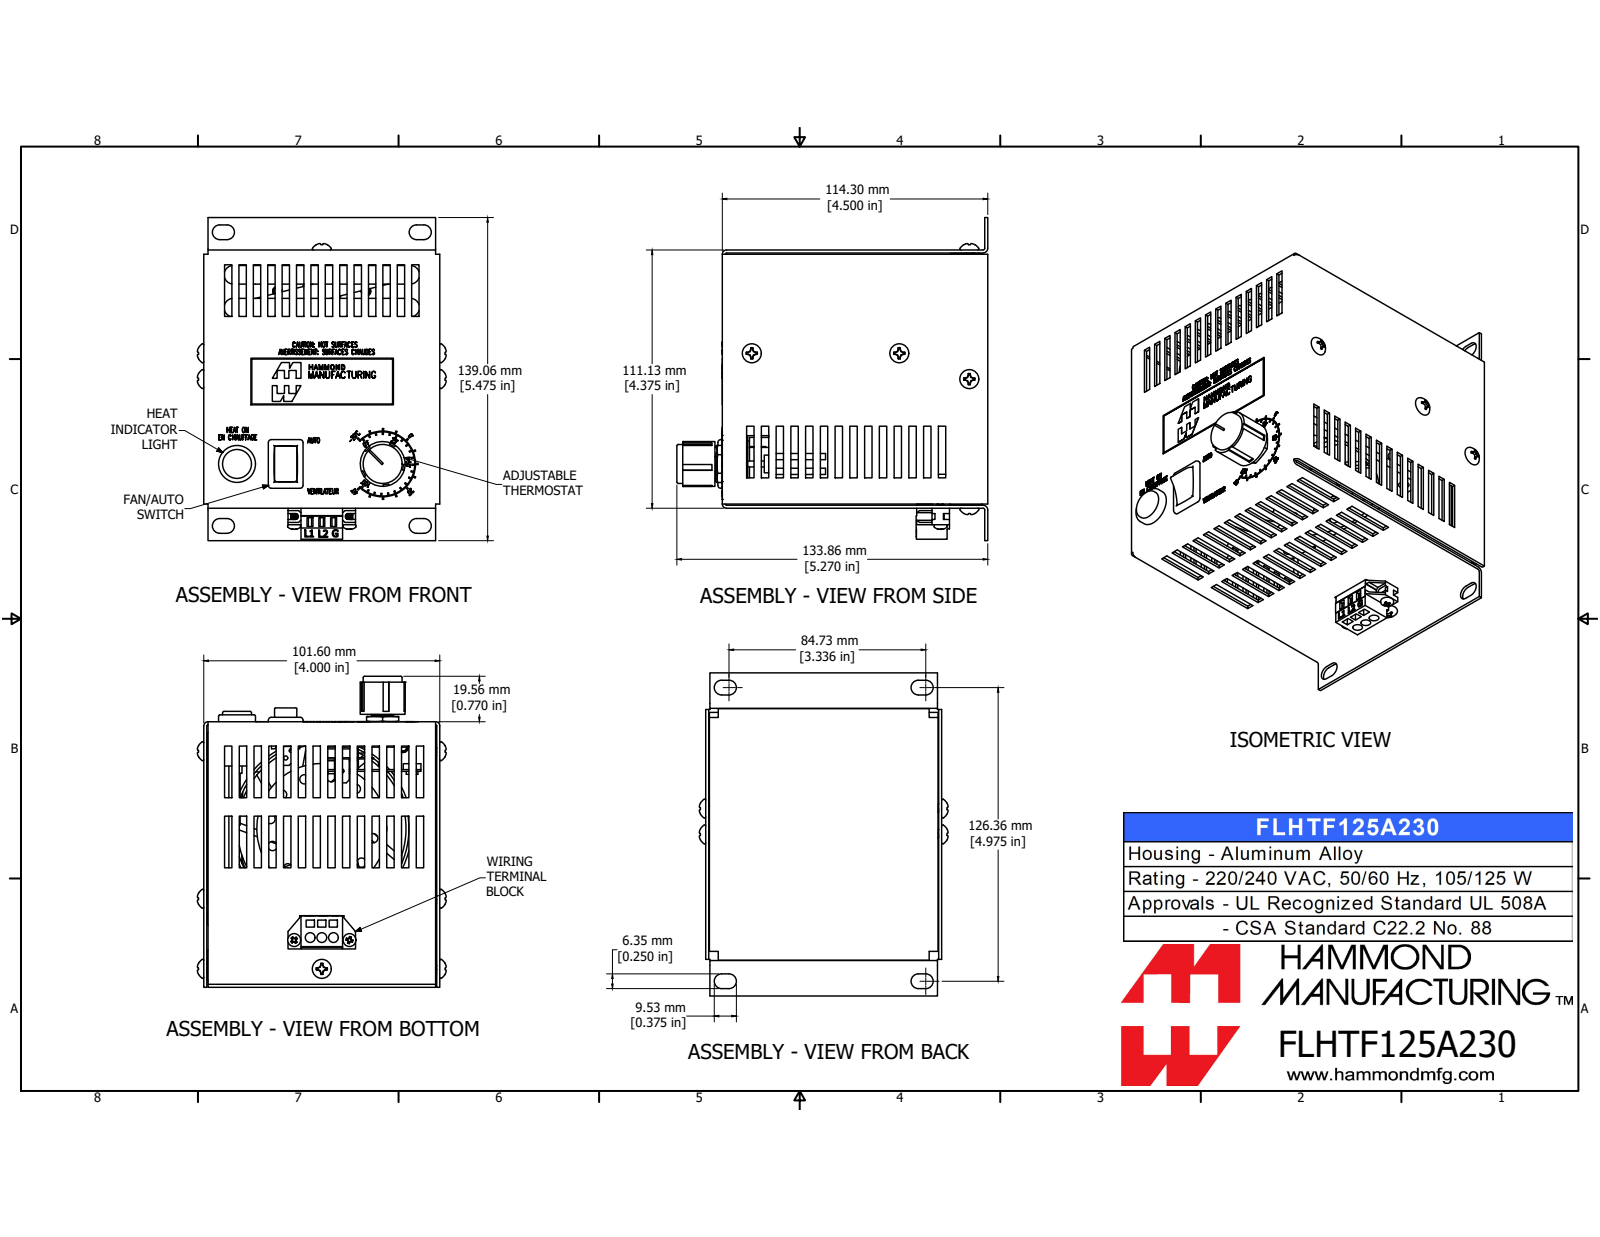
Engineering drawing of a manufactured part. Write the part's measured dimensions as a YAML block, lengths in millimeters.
part_name: "FLHTF125A230"
step_written_by: "SolidWorks 2019 (AUTOMOTIVE_DESIGN)"
units: millimeters
bodies: {solids: 17, faces: 4154, planar: 3643, cylindrical: 274, other: 237}
overall_size: [139.1, 133.9, 107.1]
volume: 143800
surface_area: 176800
round_holes:
  - {diameter: 3.5, count: 4}
  - {diameter: 4.6, count: 4}
  - {diameter: 5.2, count: 4}
  - {diameter: 4.2, count: 3}
  - {diameter: 2.2, count: 2}
  - {diameter: 3, count: 2}
  - {diameter: 3.3, count: 2}
  - {diameter: 4.8, count: 2}
  - {diameter: 1.7, count: 1}
  - {diameter: 1.8, count: 1}
  - {diameter: 6.4, count: 1}
  - {diameter: 9.7, count: 1}
round_bosses_or_shafts:
  - {diameter: 4.2, count: 4}
  - {diameter: 2.6, count: 4}
  - {diameter: 4.3, count: 2}
  - {diameter: 2.7, count: 2}
  - {diameter: 19.3, count: 1}
  - {diameter: 16.8, count: 1}
  - {diameter: 16.5, count: 1}
  - {diameter: 15.9, count: 1}
partial_cylinders:
  - {radius: 3.2, count: 38}
  - {radius: 1.3, count: 17}
  - {radius: 0.6, count: 12}
  - {radius: 16, count: 12}
  - {radius: 3.8, count: 9}
  - {radius: 0.5, count: 4}
  - {radius: 1.8, count: 4}
  - {radius: 0.4, count: 2}
face_to_face_distances: [1.3, 100.3, 2.5, 1.3, 109.8, 101.6, 99, 114.1, 111.6, 112.9]
hole_center_spacings: [70, 5, 7, 12, 13.5, 14.3, 14.4, 16.9]
